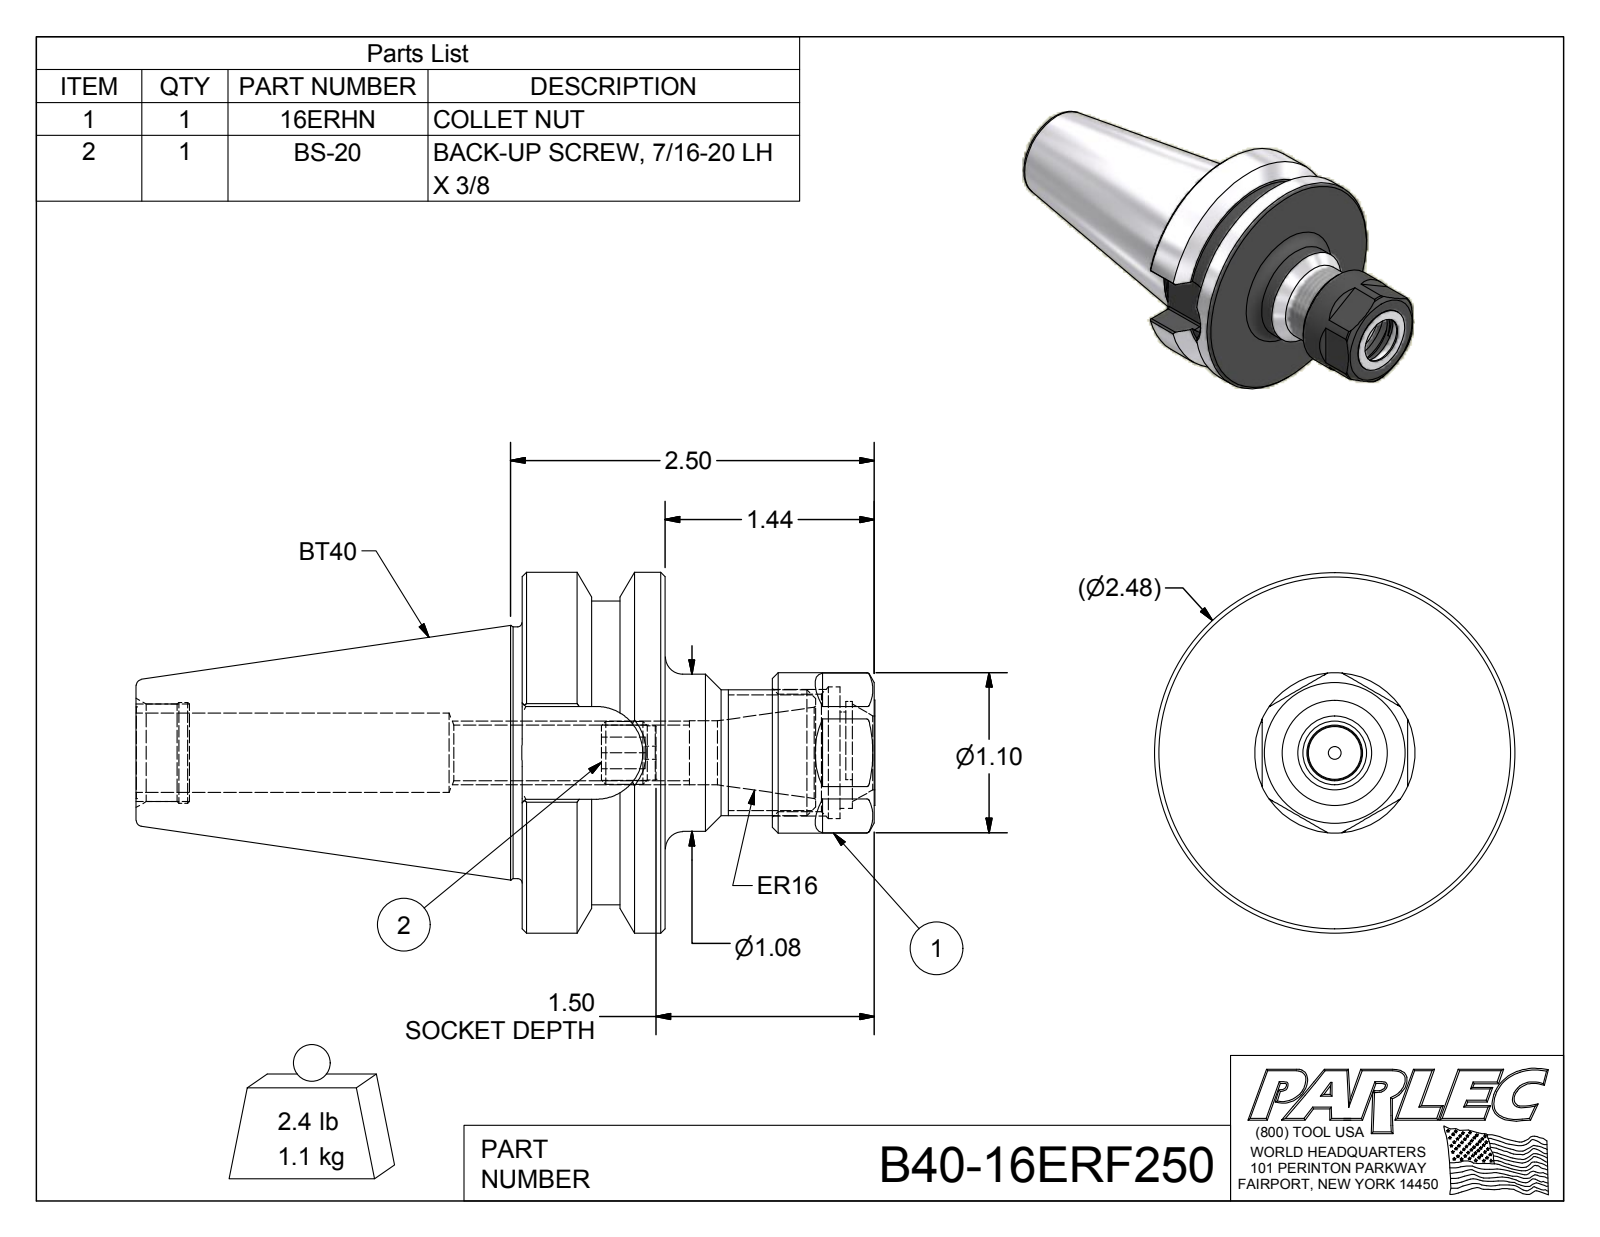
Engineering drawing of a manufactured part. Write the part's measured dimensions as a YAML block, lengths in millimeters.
part_name: "B40-16ER2-1; 16ERHN; BS-20; B40-16ERF250"
step_written_by: "Autodesk Inventor 2016 (AUTOMOTIVE_DESIGN)"
units: millimeters
bodies: {solids: 3, faces: 123, planar: 51, cylindrical: 34, other: 38}
overall_size: [128.91, 62.99, 62.99]
volume: 136631
surface_area: 29692
round_holes:
  - {diameter: 2.29, count: 1}
  - {diameter: 9.73, count: 1}
  - {diameter: 11.18, count: 1}
  - {diameter: 12.4, count: 1}
  - {diameter: 13.84, count: 1}
  - {diameter: 17.01, count: 1}
  - {diameter: 17.02, count: 1}
  - {diameter: 17.62, count: 1}
  - {diameter: 20.5, count: 1}
  - {diameter: 23, count: 1}
round_bosses_or_shafts:
  - {diameter: 62.99, count: 1}
  - {diameter: 53.01, count: 1}
  - {diameter: 43.94, count: 1}
  - {diameter: 28, count: 1}
  - {diameter: 27.43, count: 1}
  - {diameter: 22, count: 1}
  - {diameter: 17, count: 1}
  - {diameter: 10.97, count: 1}
partial_cylinders:
  - {radius: 0.51, count: 8}
  - {radius: 7.24, count: 1}
  - {radius: 8.09, count: 1}
  - {radius: 9, count: 1}
face_to_face_distances: [24.99, 61.52, 36.53, 25.14, 45.22, 67.39, 92.38, 128.91, 10.04, 35.18]
hole_center_spacings: [1.52]
